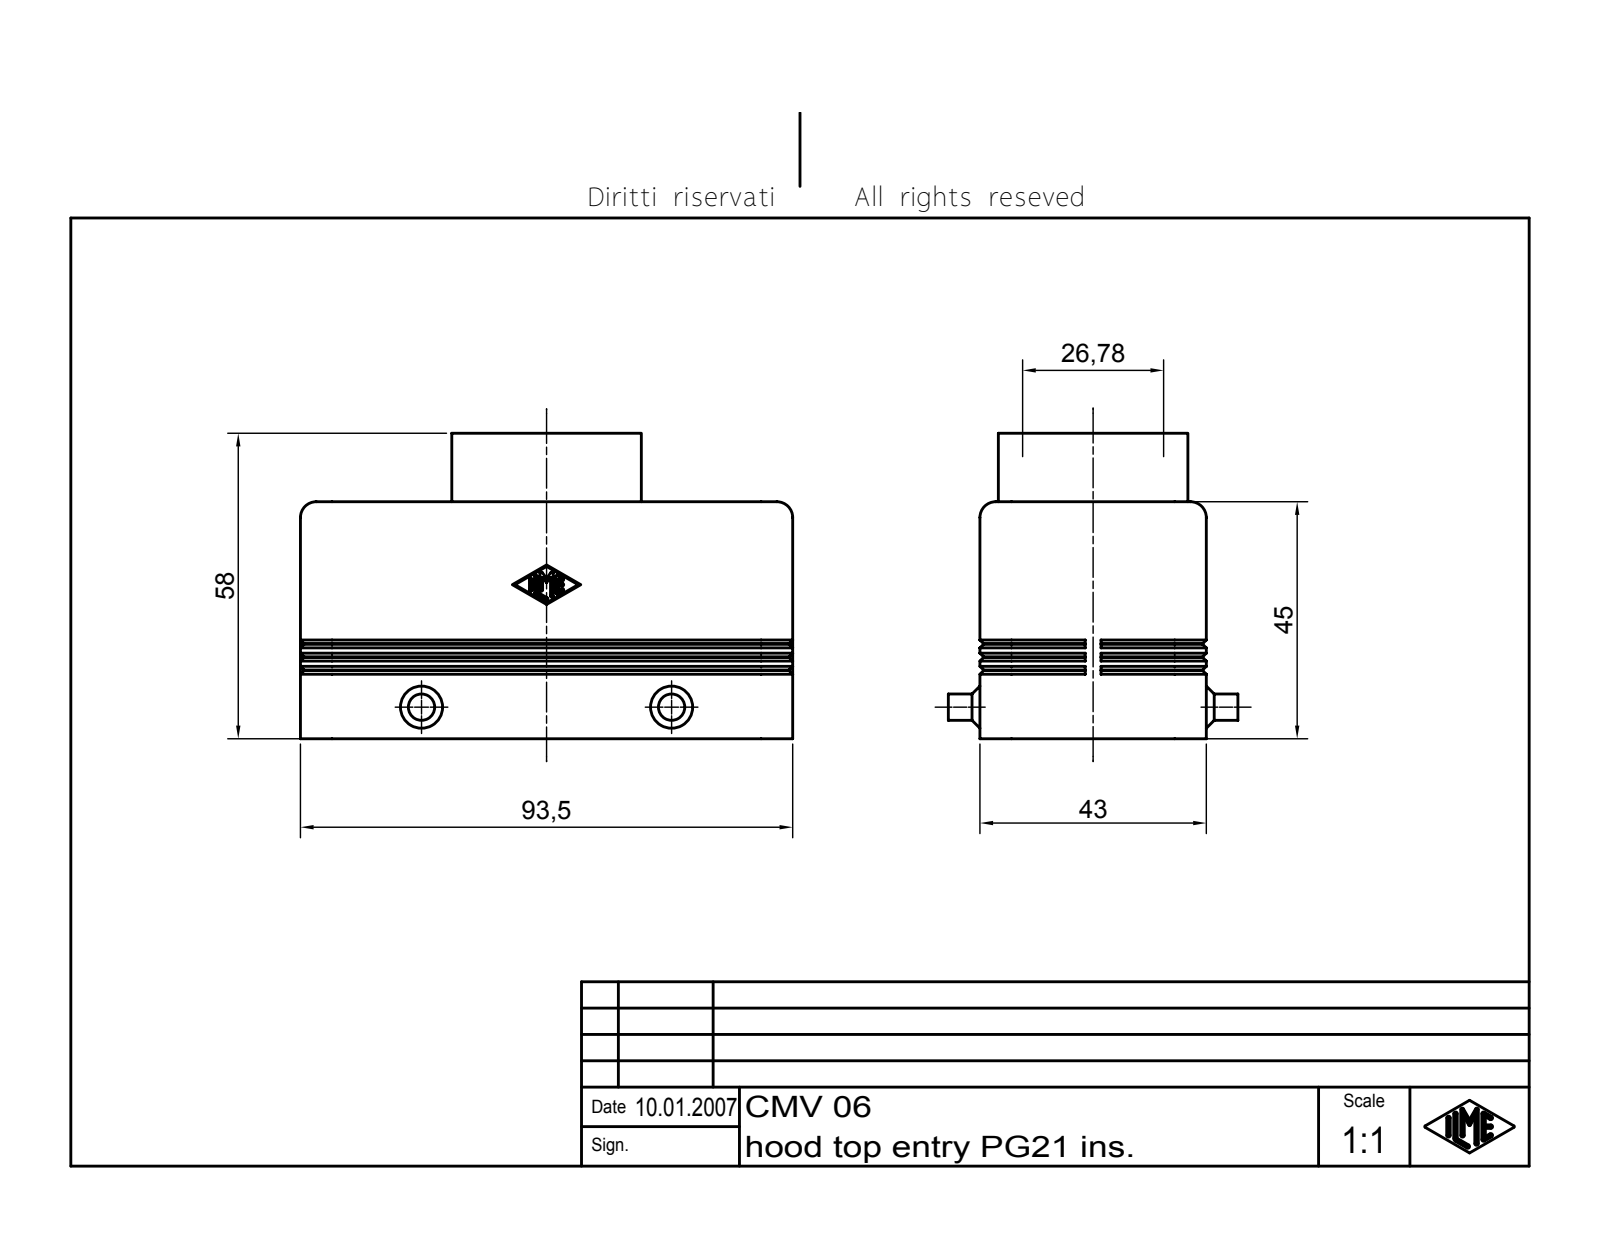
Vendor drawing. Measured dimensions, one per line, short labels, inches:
name: CHV Tüllengehäuse 2 Bügel für einen Einsatz
written by: Autodesk Inventor 7 (AUTOMOTIVE_DESIGN)
unit: in
bodies: 1 solid, 332 faces (124 planar, 83 cylindrical, 125 other)
size: 3.681 × 2.283 × 2.165
volume: 3.526 in³; area: 51.53 in²
holes: 1× ⌀0.851, 1× ⌀1.054
bosses: 2× ⌀0.197, 1× ⌀1.417
rounds: 14× R0.01, 8× R0.118, 4× R0.079, 4× R0.236, 2× R0.209, 1× R0.059
face distances: 0.118, 1.575, 1.457, 1.693, 0.453, 0.335, 3.563, 3.681, 3.445, 1.122
